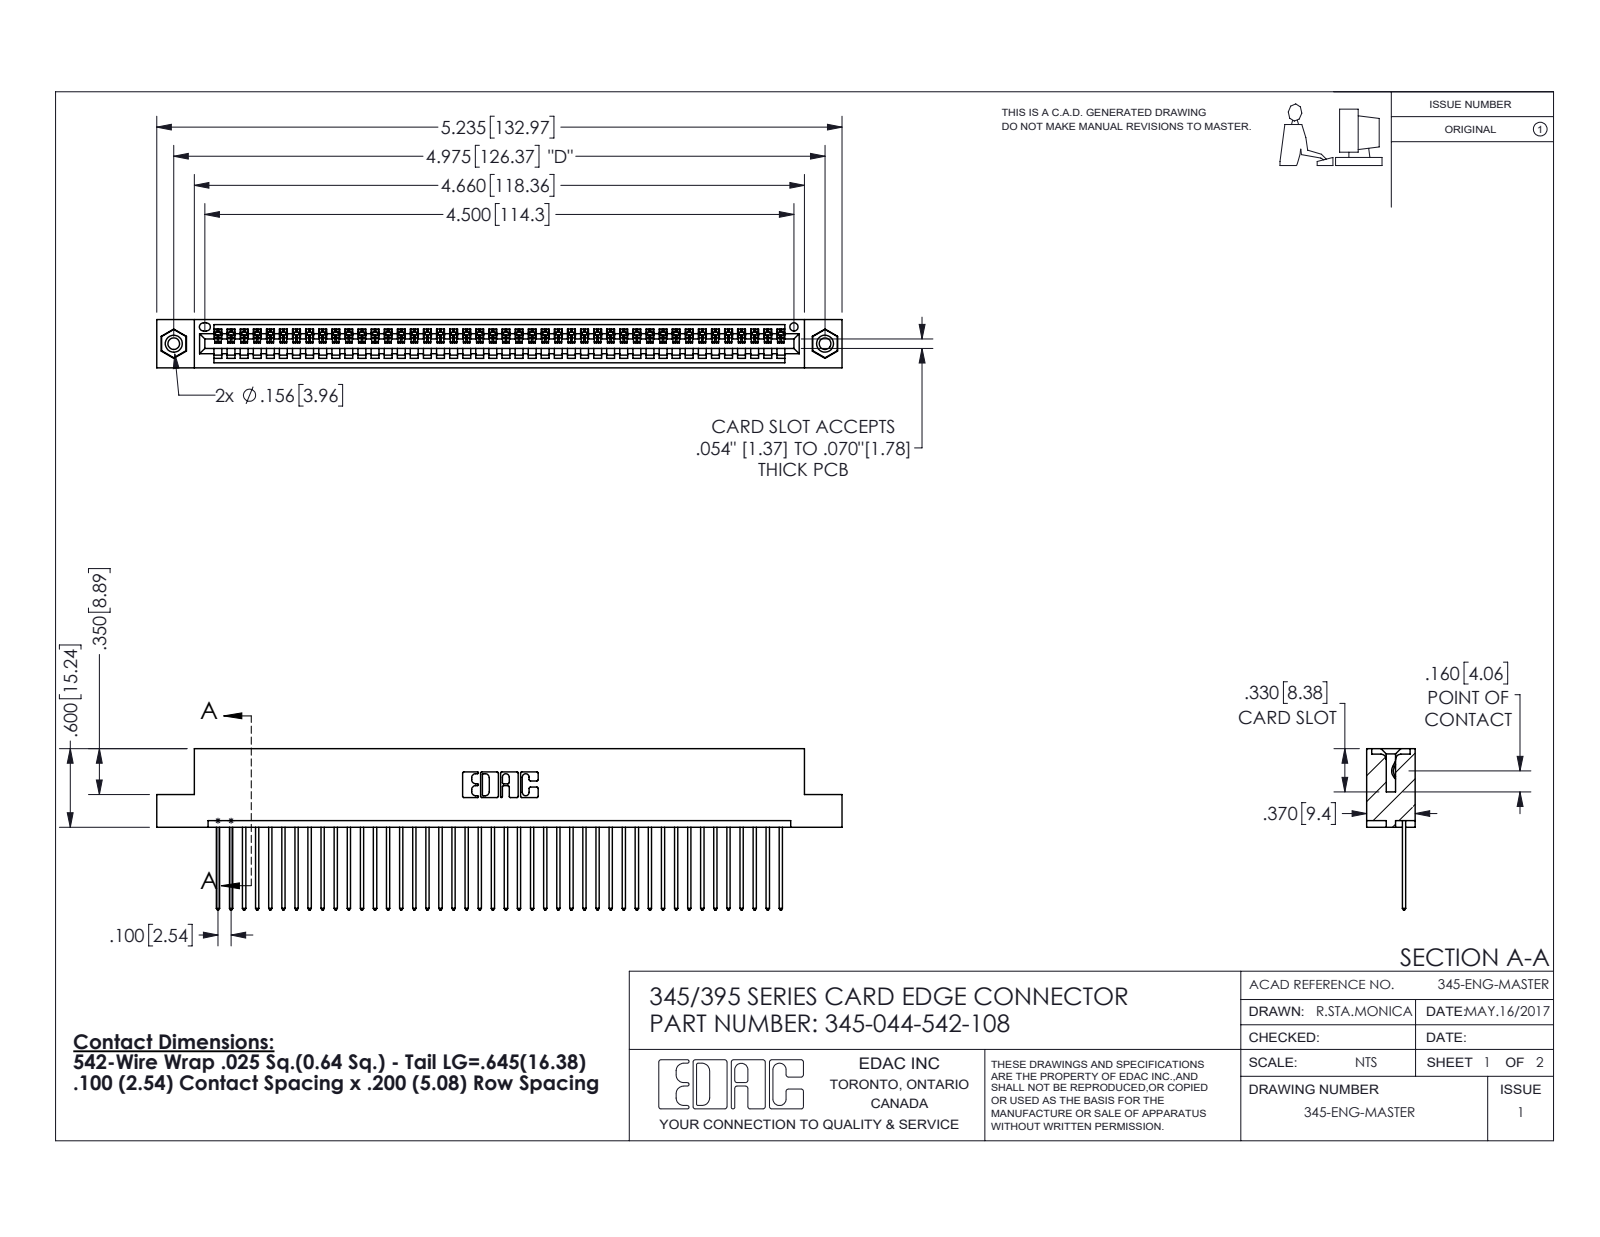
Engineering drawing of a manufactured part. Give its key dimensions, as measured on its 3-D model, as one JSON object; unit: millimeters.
{"part_name": "345-292-001_345-293-142; 345-250-001_345-250-003-102; 345-044-542-108; 345 Part_Flush Mounting Lugs - 0.156 Dia-TI", "step_written_by": "SolidWorks 2016 (CONFIG_CONTROL_DESIGN)", "units": "millimeters", "bodies": {"solids": 47, "faces": 2738, "planar": 1872, "cylindrical": 850, "other": 16}, "overall_size": [133, 31.3, 9.4], "volume_mm3": 12700, "surface_area_mm2": 17590, "round_holes": [[2.3, 2], [3.2, 2], [4, 2], [1.6, 1]], "round_bosses_or_shafts": [[3.9, 2]], "partial_cylinders_radius": [[0.2, 88], [0.3, 88], [0.3, 22], [0.2, 6], [0.8, 6], [0.7, 3], [0.8, 2], [1, 2]], "face_to_face_distances": [1.8, 7.6, 9.4, 2.5, 6.9, 0.6, 5.1, 5.7, 3.8, 1.8], "hole_center_spacings": [6.9, 120.4, 126.4]}
